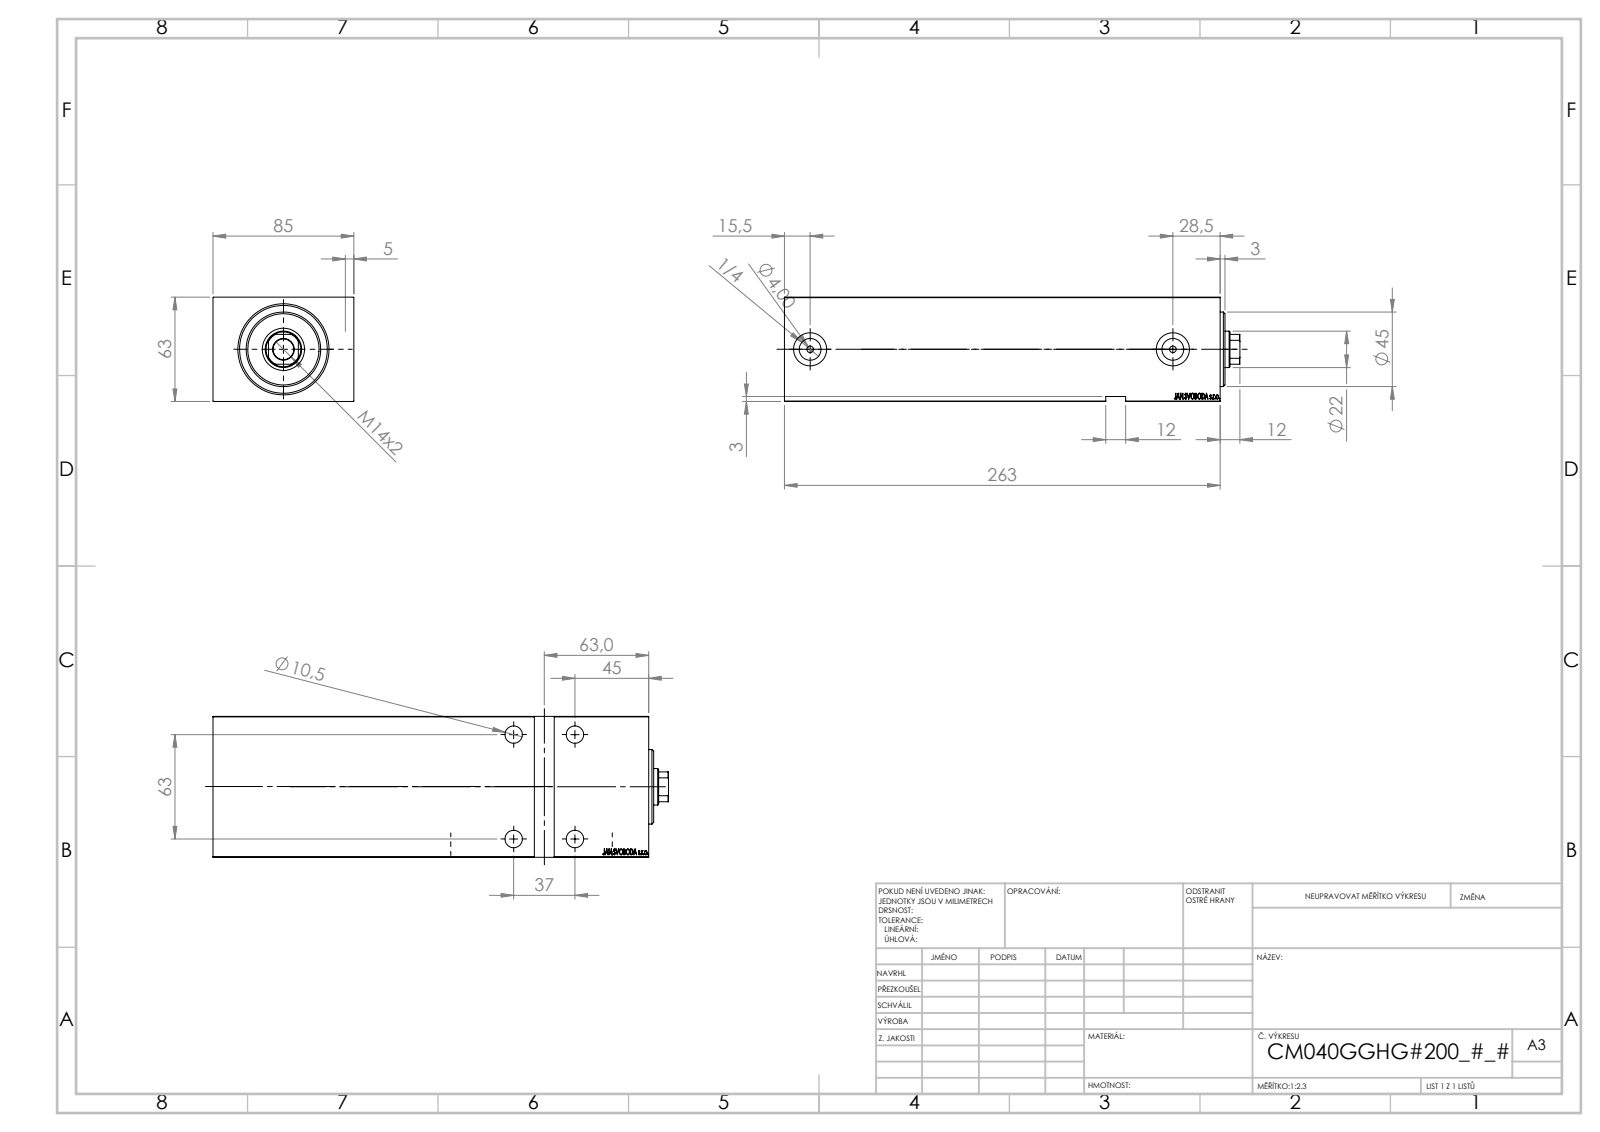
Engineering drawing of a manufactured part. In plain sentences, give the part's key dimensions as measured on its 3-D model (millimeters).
The part is named "V450CM_G_VCP; Zatka_OIL_PORT; V450CM_VC_G; V450CM_G_Body". Its 3-D file was written by "SolidWorks 2019 (CONFIG_CONTROL_DESIGN)". It is 5 solids with 897 faces: 441 planar, 58 cylindrical and 398 other. Overall it measures 275 by 85 by 63 millimeters. Its volume is 1 197 000 cubic millimeters and its surface area 162 561 square millimeters. Round holes: 4 of diameter 10.5, 4 of diameter 16.5, 2 of diameter 4, 2 of diameter 13.16, 2 of diameter 20, 1 of diameter 12.5, 1 of diameter 22, 1 of diameter 25.5, 1 of diameter 40, 1 of diameter 42, 1 of diameter 53. Round bosses or shafts: 2 of diameter 18, 1 of diameter 45, 1 of diameter 27. Partial cylindrical surfaces (rounded edges, fillets, slot ends): 1 of radius 10.5. The main face-to-face distances are 63, 85, 263, 12, 251, 5, 258, 246, 3, 60. The hole center spacings are 37, 63, 73.06, 219.
